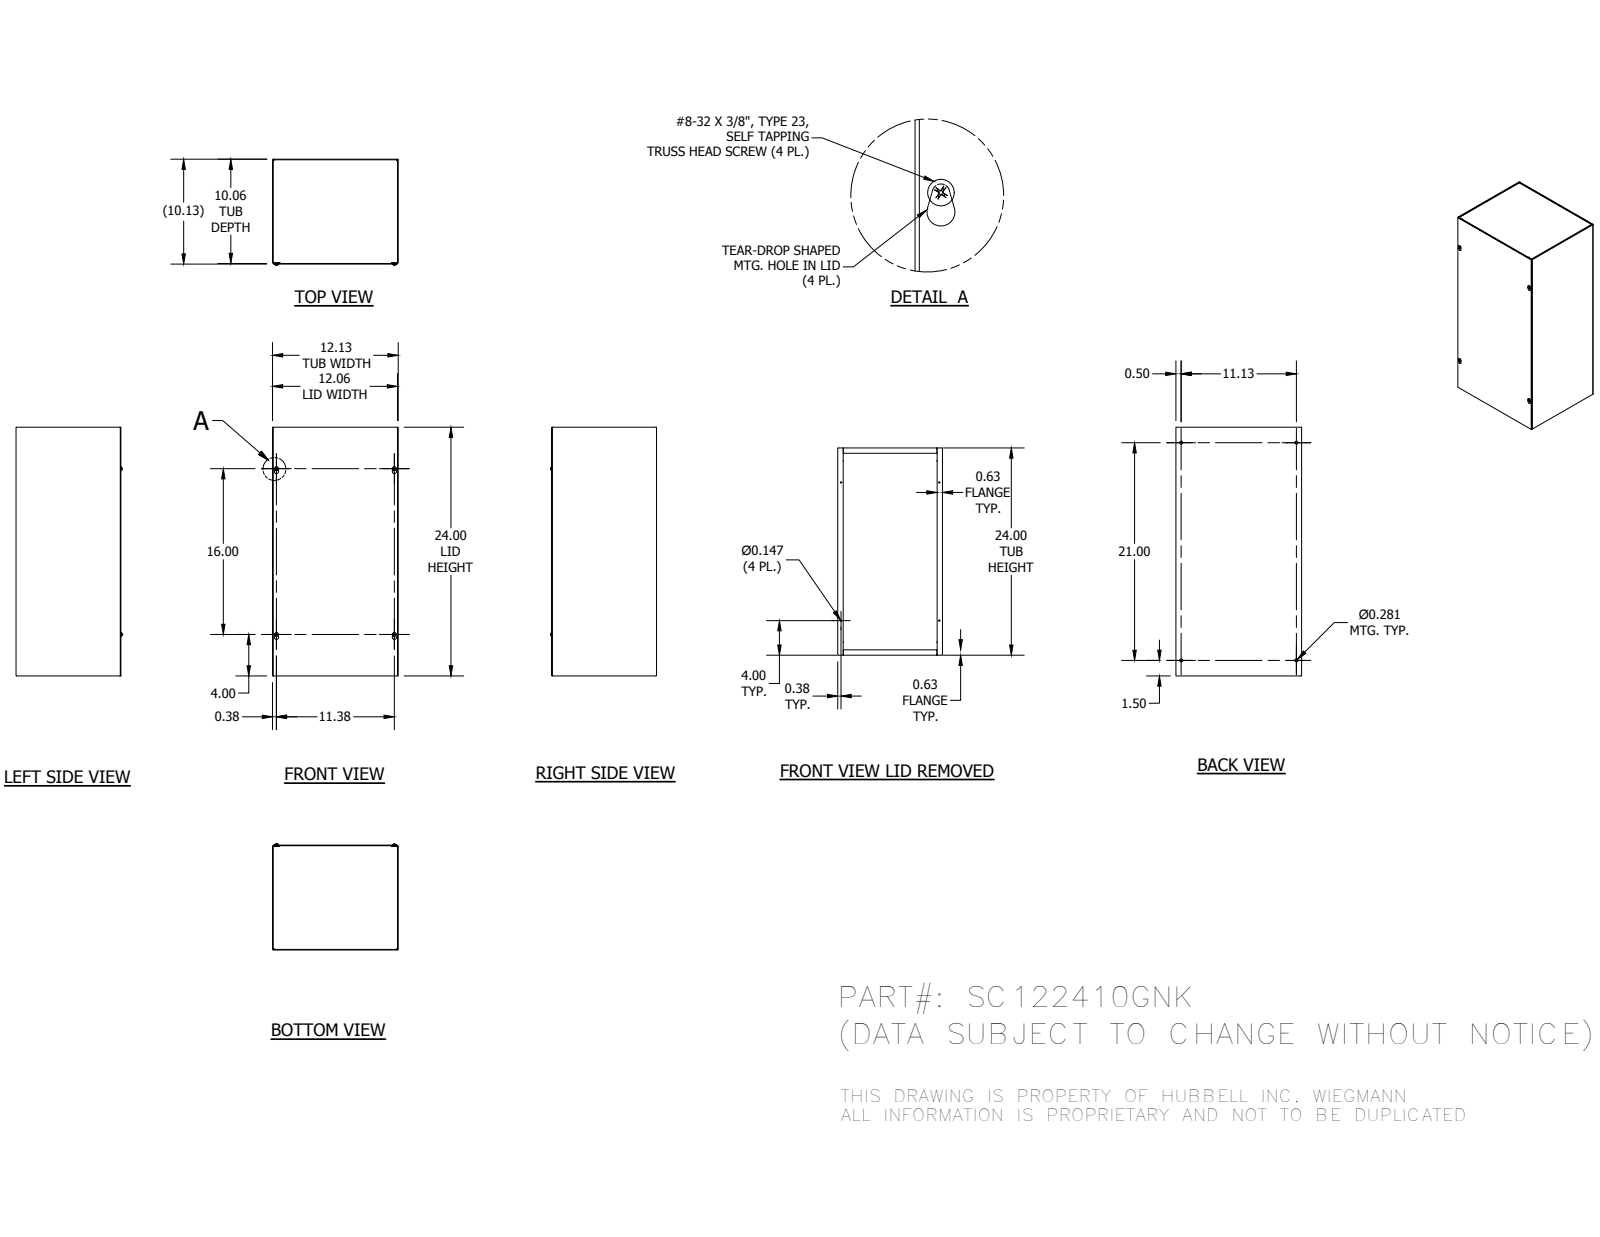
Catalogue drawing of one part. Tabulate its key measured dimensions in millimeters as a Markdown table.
| quantity | value |
| --- | --- |
| part name | SC122410GNKBLR; SC1210GNKTB; SC1224GLPA; 34056 (+1 more) |
| STEP written by | Autodesk Inventor 2014 (AUTOMOTIVE_DESIGN) |
| units | millimeters |
| bodies | 8 solids, 268 faces (152 planar, 48 cylindrical, 68 other) |
| overall size | 609.6 × 307.98 × 259.72 |
| volume | 1 403 000 mm³ |
| surface area | 1 779 000 mm² |
| round holes (diameter × count) | 3.73 × 4, 7.14 × 4 |
| round bosses / shafts (diameter × count) | 9.75 × 4, 4.17 × 4 |
| partial cylindrical surfaces (radius × count) | 0.4 × 12, 1.98 × 12, 3.17 × 4, 5.16 × 4 |
| main face-to-face distances | 1.59, 306.39, 254, 1.58, 255.59, 255.58, 257.17, 304.8, 307.98, 608.01 |
| hole center spacings | 63.58, 292.72, 469.91, 549.96, 282.58, 288.92, 406.4, 498.63 |
